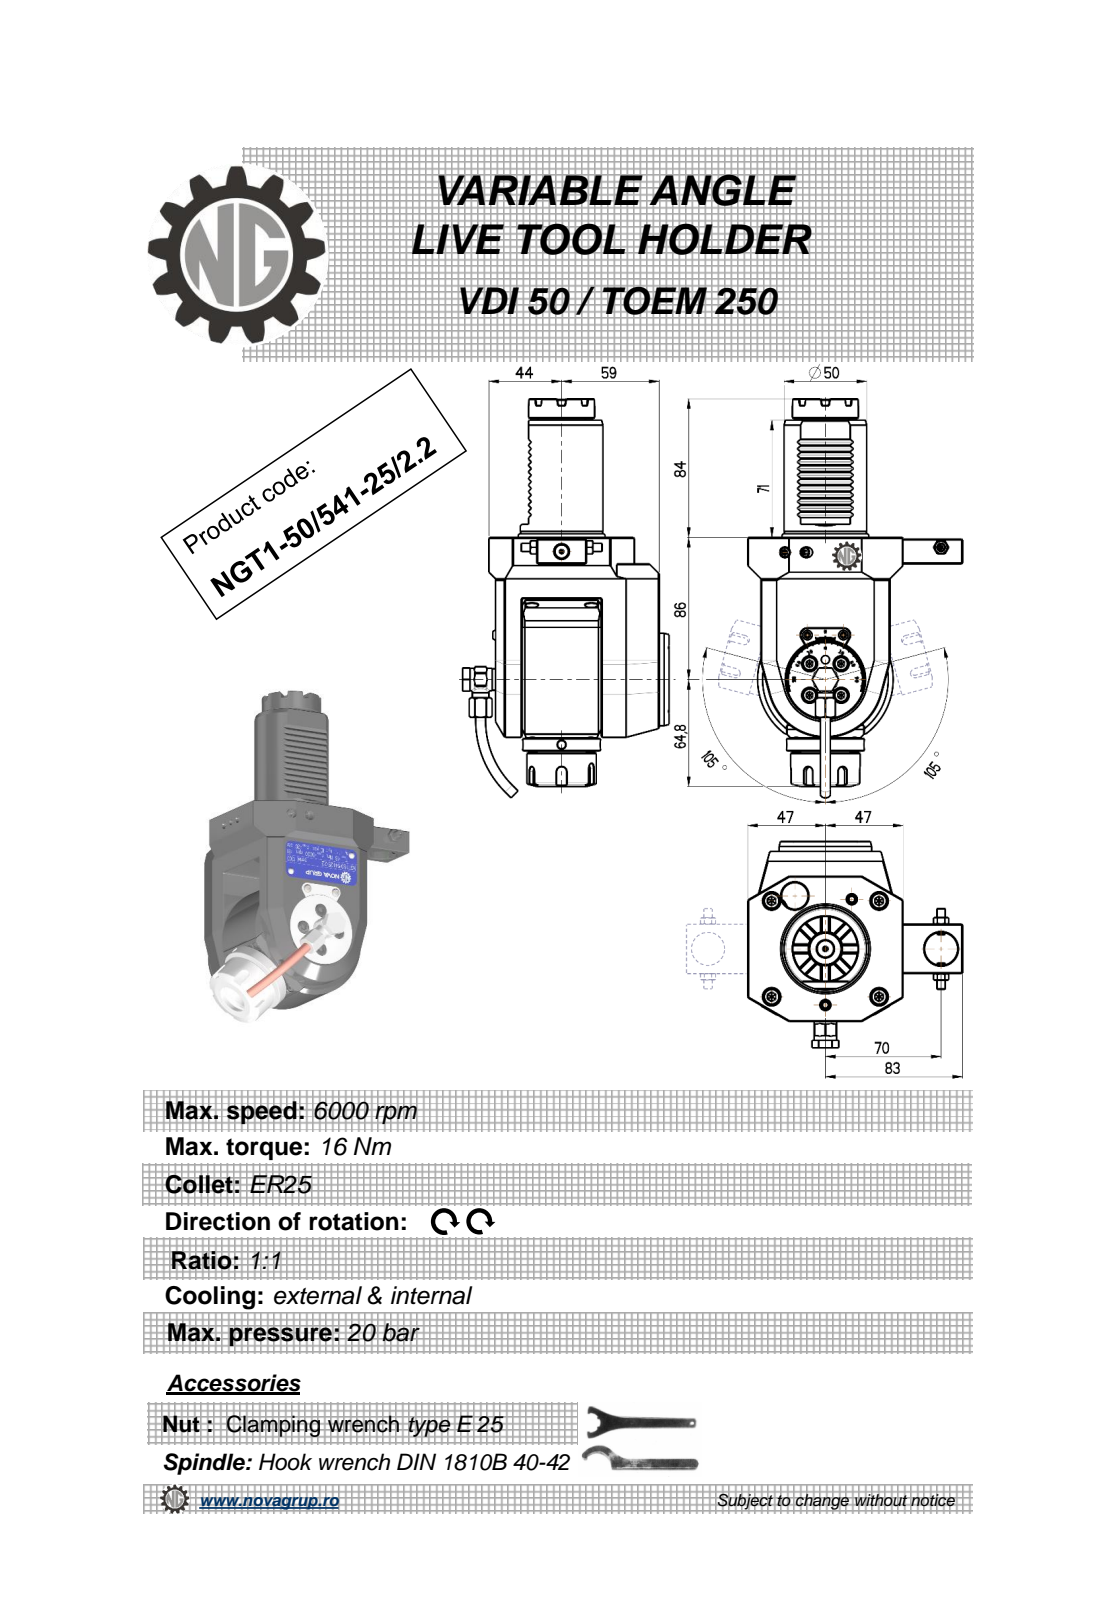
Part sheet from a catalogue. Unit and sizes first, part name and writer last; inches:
Units: inches
Overall size (bounding box): 9.515 × 5.118 × 4.917
Round holes (diameter × count): ⌀0.157 ×3, ⌀0.197 ×2, ⌀0.118 ×1, ⌀0.244 ×1, ⌀0.354 ×1, ⌀0.374 ×1, ⌀0.394 ×1, ⌀0.433 ×1, ⌀0.787 ×1, ⌀0.799 ×1
Round bosses / shafts (diameter × count): ⌀0.236 ×2, ⌀0.224 ×2, ⌀2.205 ×1, ⌀1.969 ×1, ⌀1.85 ×1, ⌀1.654 ×1, ⌀1.575 ×1, ⌀1.378 ×1
Partial cylindrical surfaces — rounded edges, fillets, slot ends (radius × count): R0.01 ×12, R0.012 ×12, R0.006 ×6, R0.118 ×5, R0.02 ×4, R0.039 ×2, R0.394 ×2, R0.303 ×1
Main face-to-face distances: 1.457, 3.898, 0.63, 0.315, 0.236, 0.827, 2.52, 4.134, 0.787, 0.157
Hole centre spacings: 0.016, 1.553, 1.929, 1.945, 2.756, 3.364, 3.373, 4.604
Volume: 63.4 in³ · Surface area: 144.4 in²
Bodies: 1 solid, 684 faces (310 planar, 140 cylindrical, 234 other)
Part name (STEP PRODUCT): NGT1_50_541_25_2_2
STEP written by: PRO/ENGINEER BY PARAMETRIC TECHNOLOGY CORPORATION, 2010280 (CONFIG_CONTROL_DESIGN)
